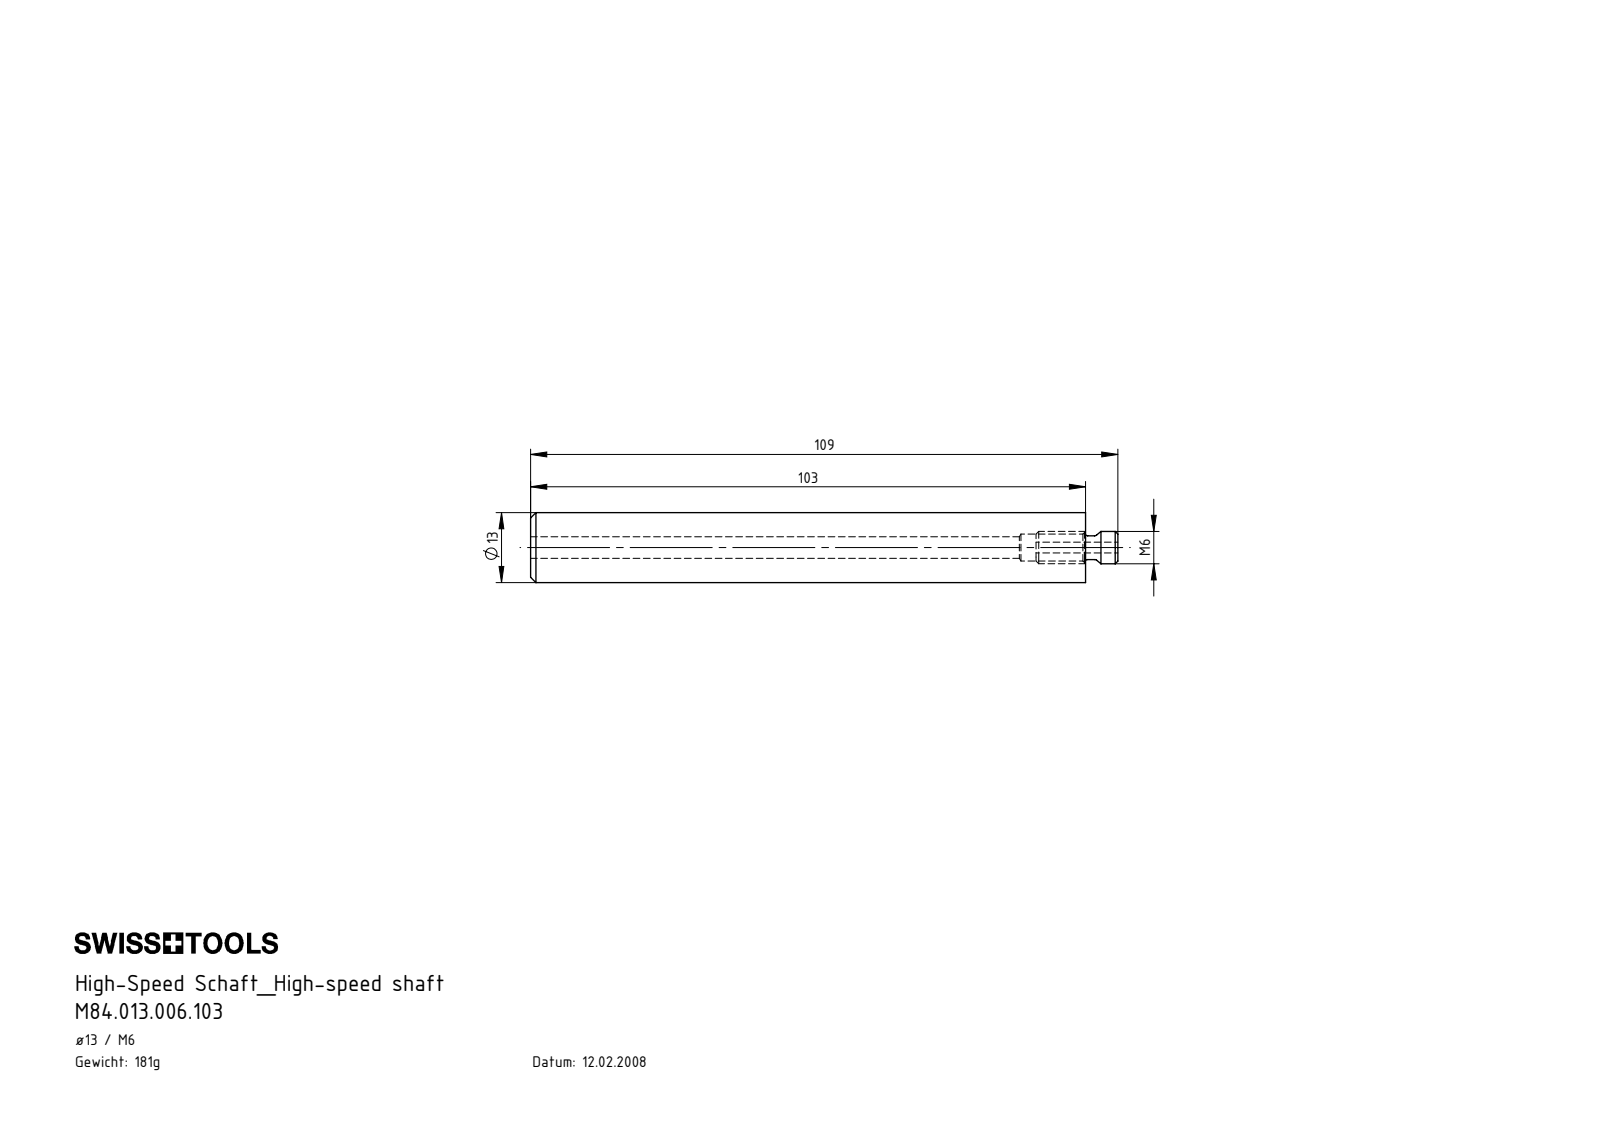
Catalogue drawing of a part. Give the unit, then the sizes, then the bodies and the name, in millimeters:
Units: millimetres
Overall size (bounding box): 109 × 13 × 13
Round holes (diameter × count): ⌀2 ×1, ⌀4 ×1, ⌀5 ×1
Round bosses / shafts (diameter × count): ⌀13 ×1, ⌀6 ×1, ⌀4.4 ×1
Main face-to-face distances: 103, 93.8, 9.2, 109, 15.2, 6, 102.8, 9, 6.2
Volume: 12 615 mm³ · Surface area: 6 169 mm²
Bodies: 2 solids, 20 faces (5 planar, 7 cylindrical, 8 other)
Part name (STEP PRODUCT): HM1-BG1.006.015_A; U13.HS6.K01.103; HM1-U13.001.103_A
STEP written by: SolidWorks 2017 (AUTOMOTIVE_DESIGN)
